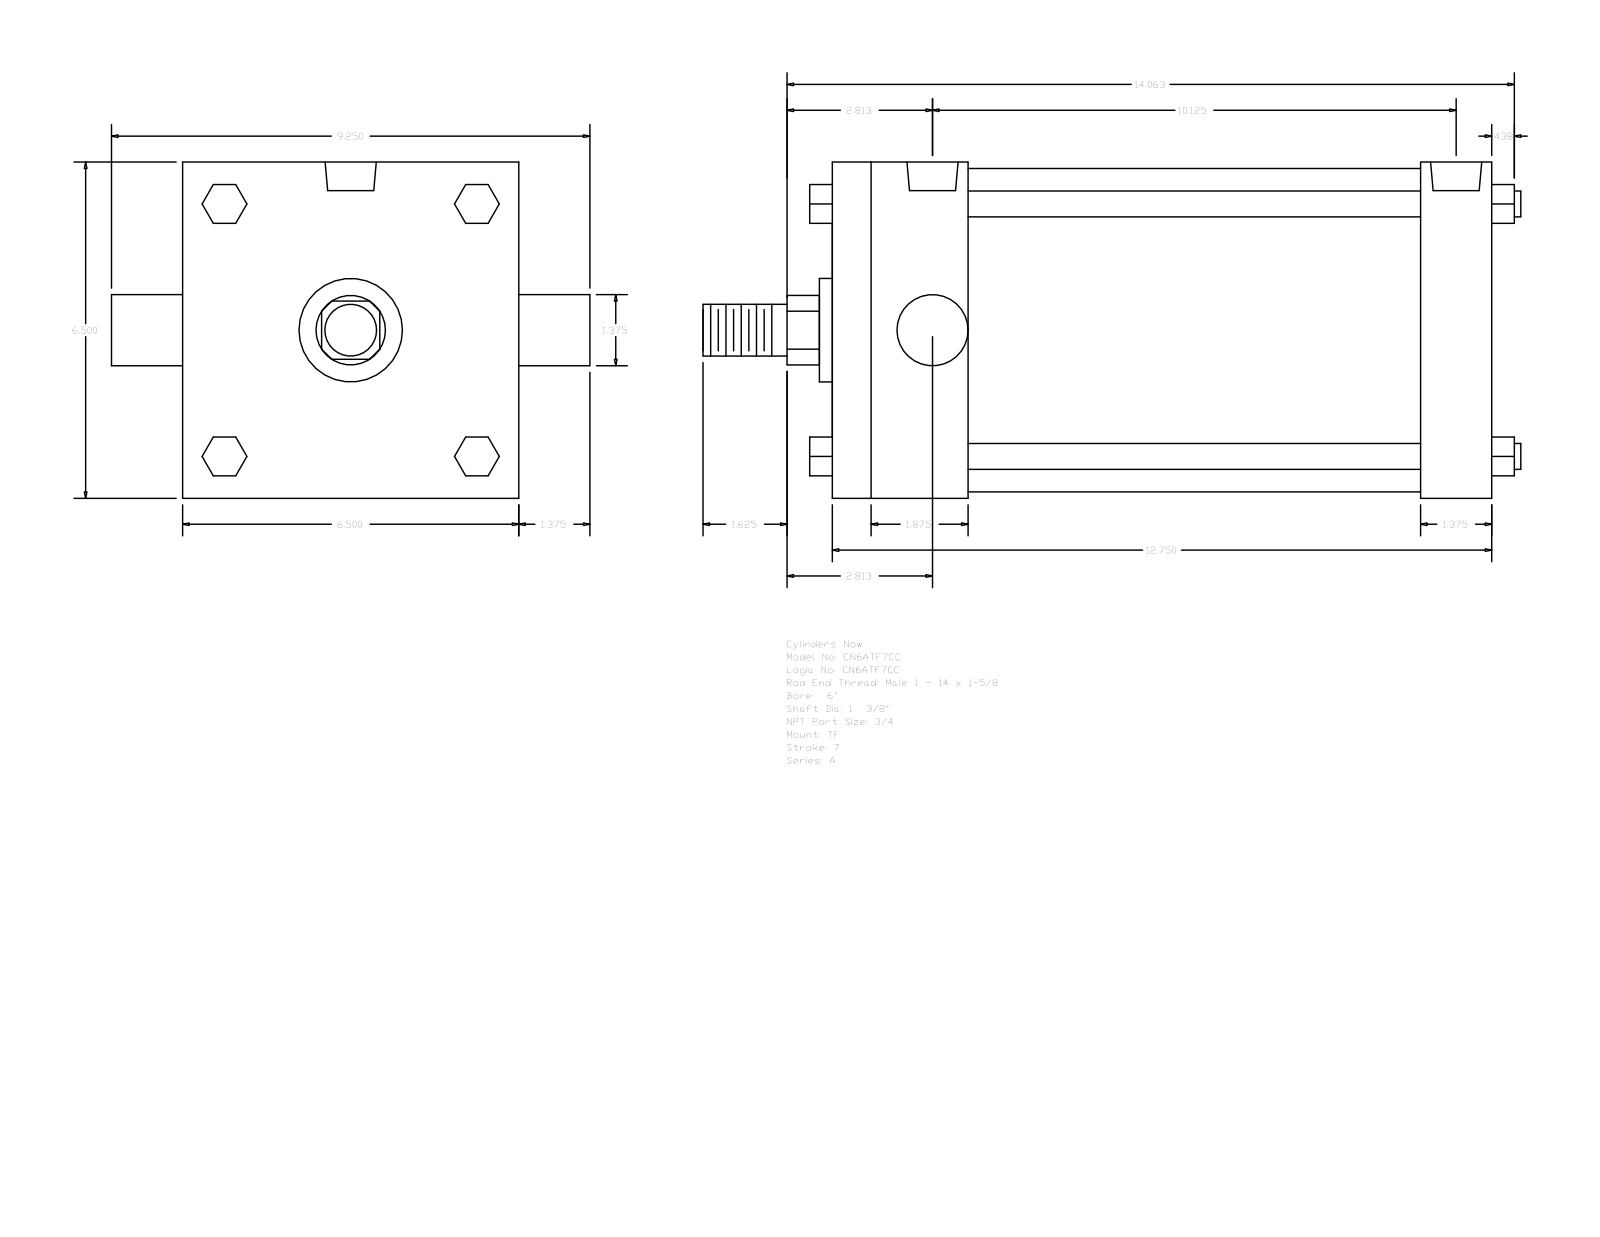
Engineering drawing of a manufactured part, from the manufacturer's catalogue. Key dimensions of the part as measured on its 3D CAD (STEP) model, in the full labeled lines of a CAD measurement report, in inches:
Part name (STEP PRODUCT): A_TF__0600_1.375
STEP written by: GSSL Pune (CONFIG_CONTROL_DESIGN)
Units: inches
Bodies: 0 solids, 120 faces (92 planar, 28 cylindrical, 0 other)
Overall size (bounding box): 15.813 × 9.25 × 6.5
Round holes (diameter × count): ⌀0.594 ×3, ⌀0.989 ×2
Round bosses / shafts (diameter × count): ⌀0.5 ×4, ⌀1.375 ×2, ⌀6.25 ×1, ⌀2 ×1, ⌀1 ×1
Partial cylindrical surfaces — rounded edges, fillets, slot ends (radius × count): R0.672 ×1
Main face-to-face distances: 6.5, 12.75, 1.375, 2.625, 10.125, 11.375, 8.75, 0.75, 2.44, 4.226
Hole centre spacings: 0.219, 9.906, 9.687, 10.125
